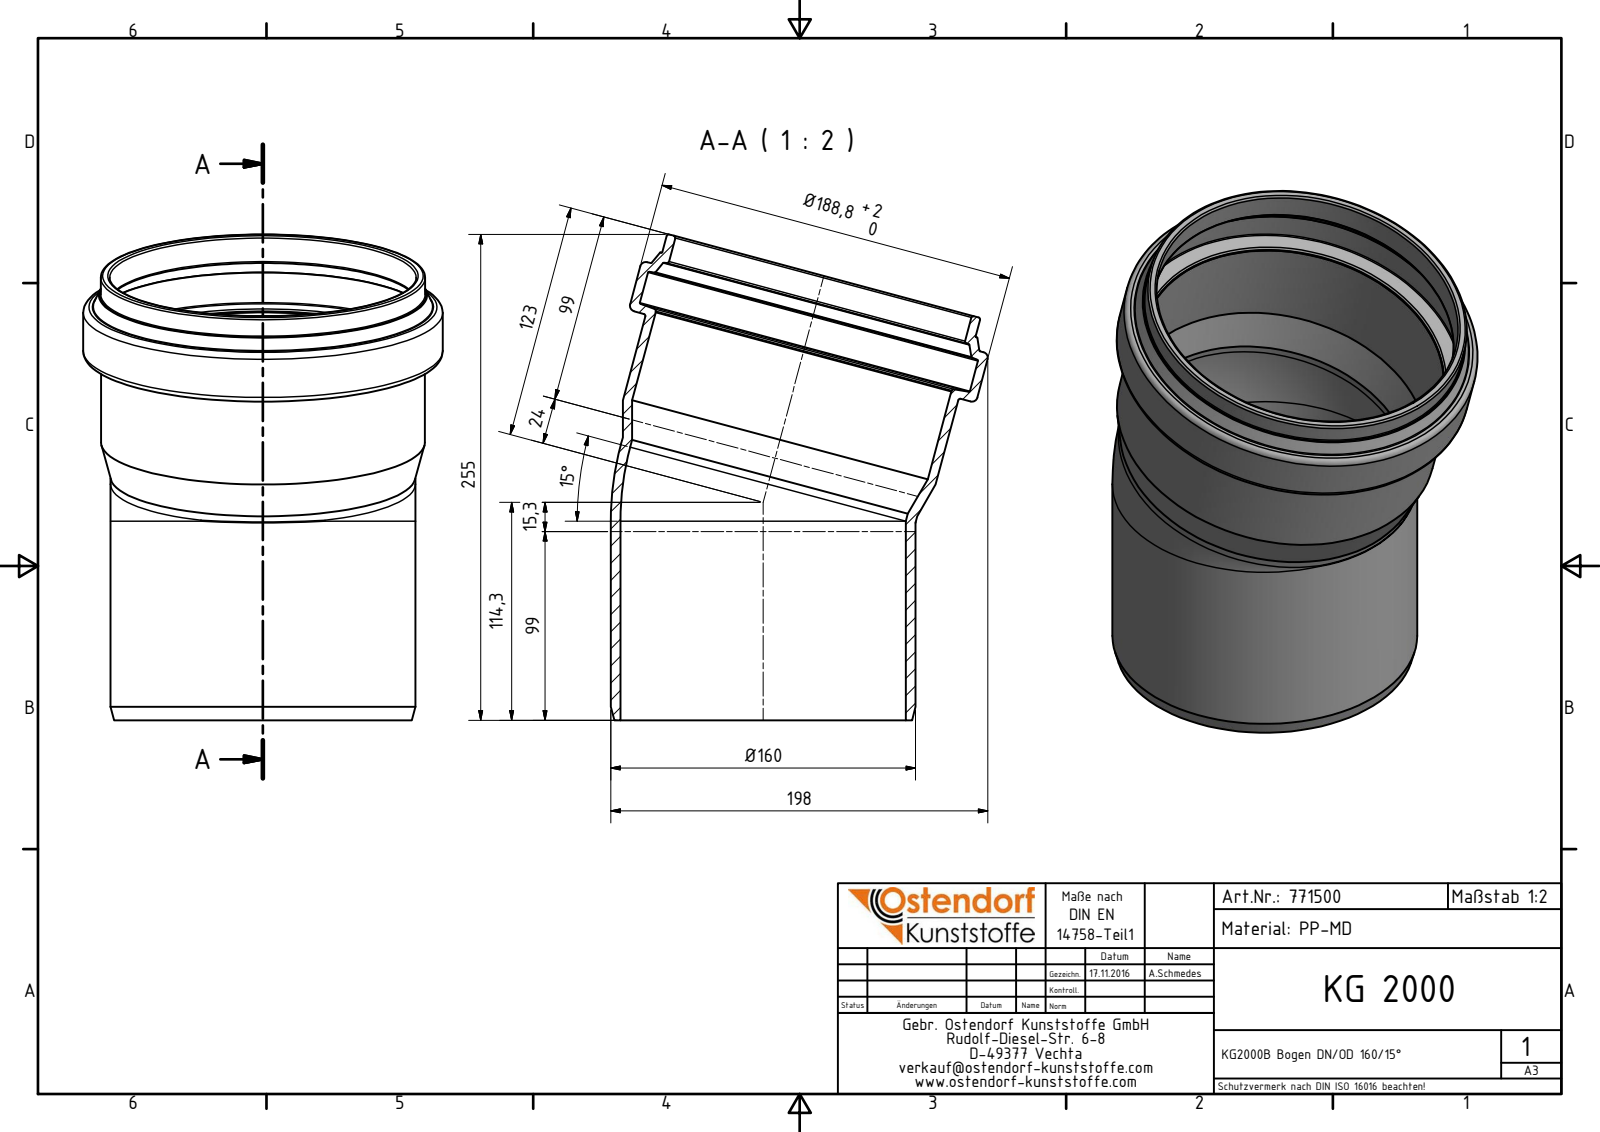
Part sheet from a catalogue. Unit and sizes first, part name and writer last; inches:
Units: inches
Overall size (bounding box): 10.039 × 7.795 × 7.433
Round holes (diameter × count): ⌀5.902 ×2, ⌀6.339 ×2, ⌀6.327 ×1, ⌀7.063 ×1
Round bosses / shafts (diameter × count): ⌀6.303 ×2, ⌀7.433 ×1, ⌀6.709 ×1, ⌀6.697 ×1
Main face-to-face distances: 1.721, 1.051, 0.67, 1.315, 0.264, 0.406, 0.096, 0.955, 1.219, 1.625
Volume: 37.99 in³ · Surface area: 402.1 in²
Bodies: 1 solid, 42 faces (6 planar, 11 cylindrical, 25 other)
Part name (STEP PRODUCT): 771500 KG2000B Bogen DN_OD 160_15°
STEP written by: Autodesk Inventor 2016 (AUTOMOTIVE_DESIGN)
